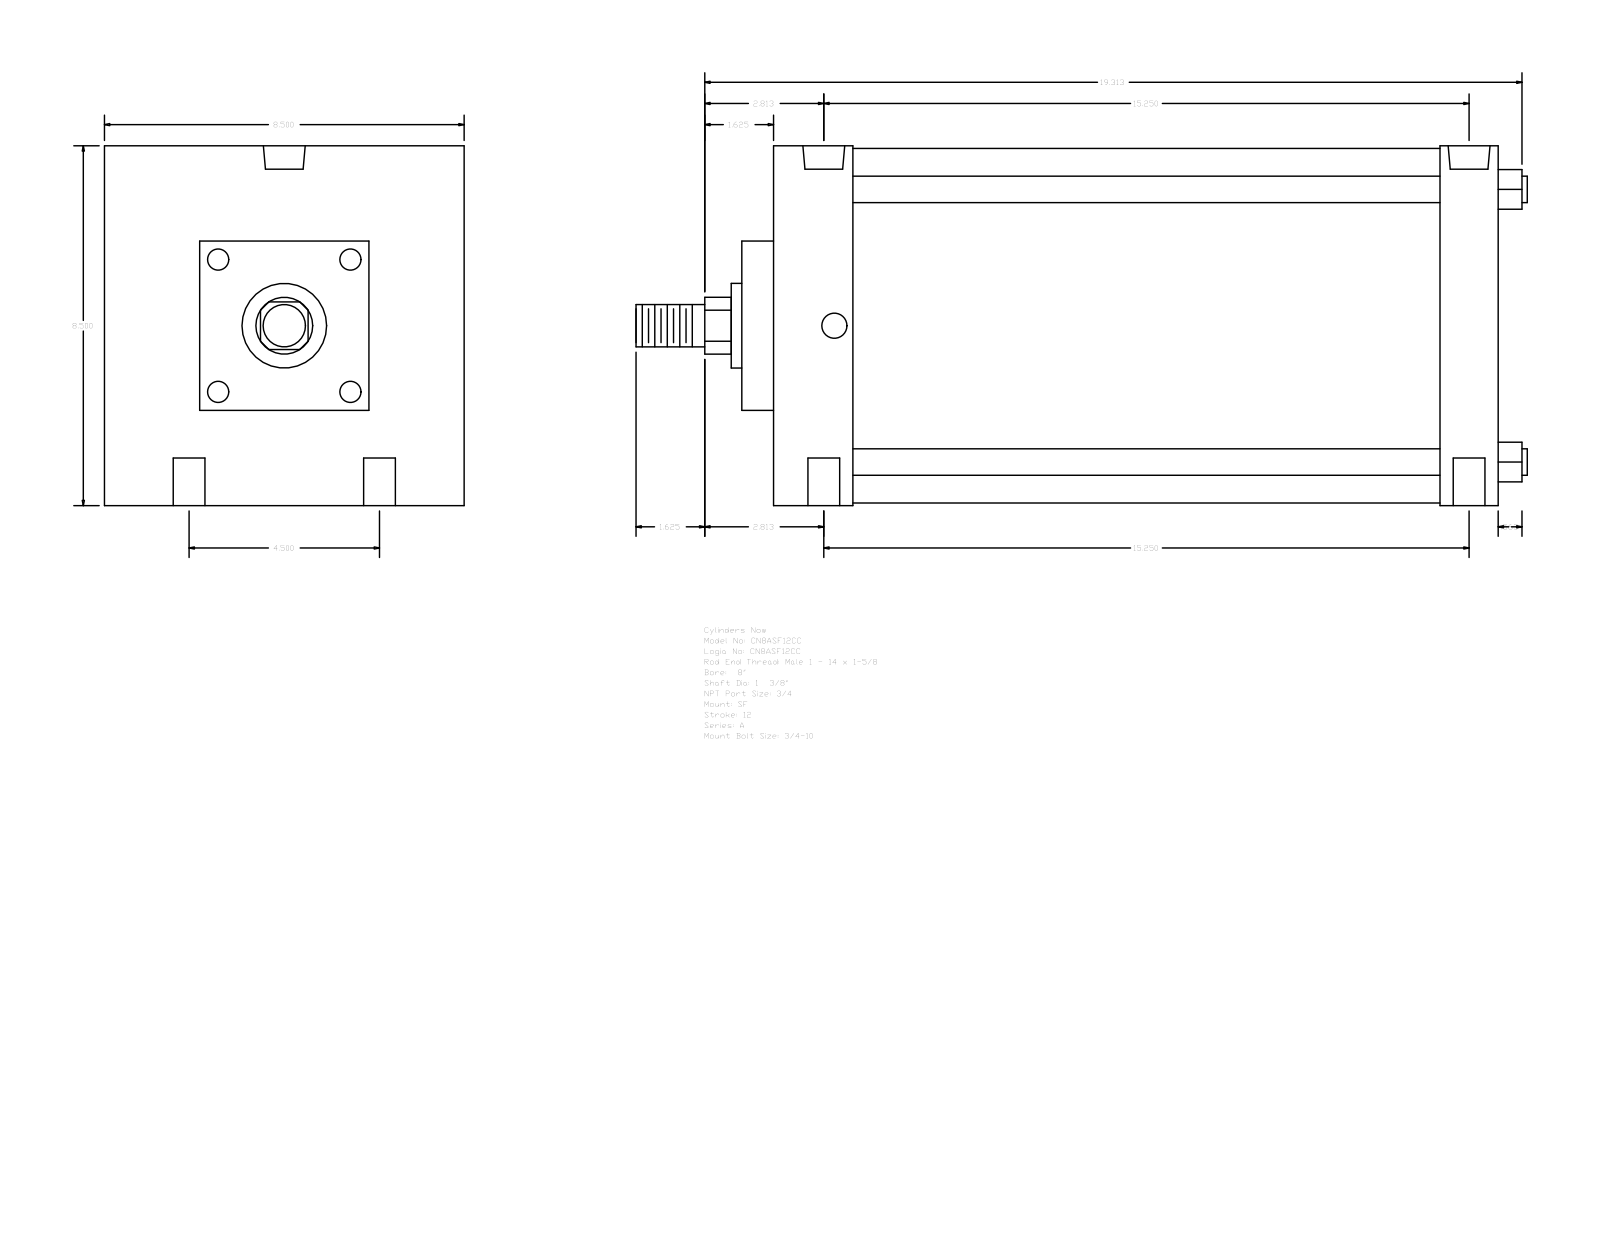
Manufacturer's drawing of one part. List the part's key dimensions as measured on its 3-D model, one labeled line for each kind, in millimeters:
Part name (STEP PRODUCT): A_SF__0800_1.375
STEP written by: GSSL Pune (CONFIG_CONTROL_DESIGN)
Units: millimetres
Bodies: 0 solids, 93 faces (67 planar, 26 cylindrical, 0 other)
Overall size (bounding box): 534.99 × 215.9 × 215.9
Round holes (diameter × count): ⌀19.05 ×4, ⌀15.08 ×2, ⌀25.12 ×2
Round bosses / shafts (diameter × count): ⌀15.88 ×4, ⌀212.72 ×1, ⌀50.8 ×1, ⌀34.92 ×1, ⌀25.4 ×1
Partial cylindrical surfaces — rounded edges, fillets, slot ends (radius × count): R17.06 ×1
Main face-to-face distances: 434.98, 215.9, 47.63, 400.05, 352.42, 387.35, 34.93, 19.04, 66.67, 419.09
Hole centre spacings: 57.15, 391.54, 387.35, 114.3, 403.86, 374.65
